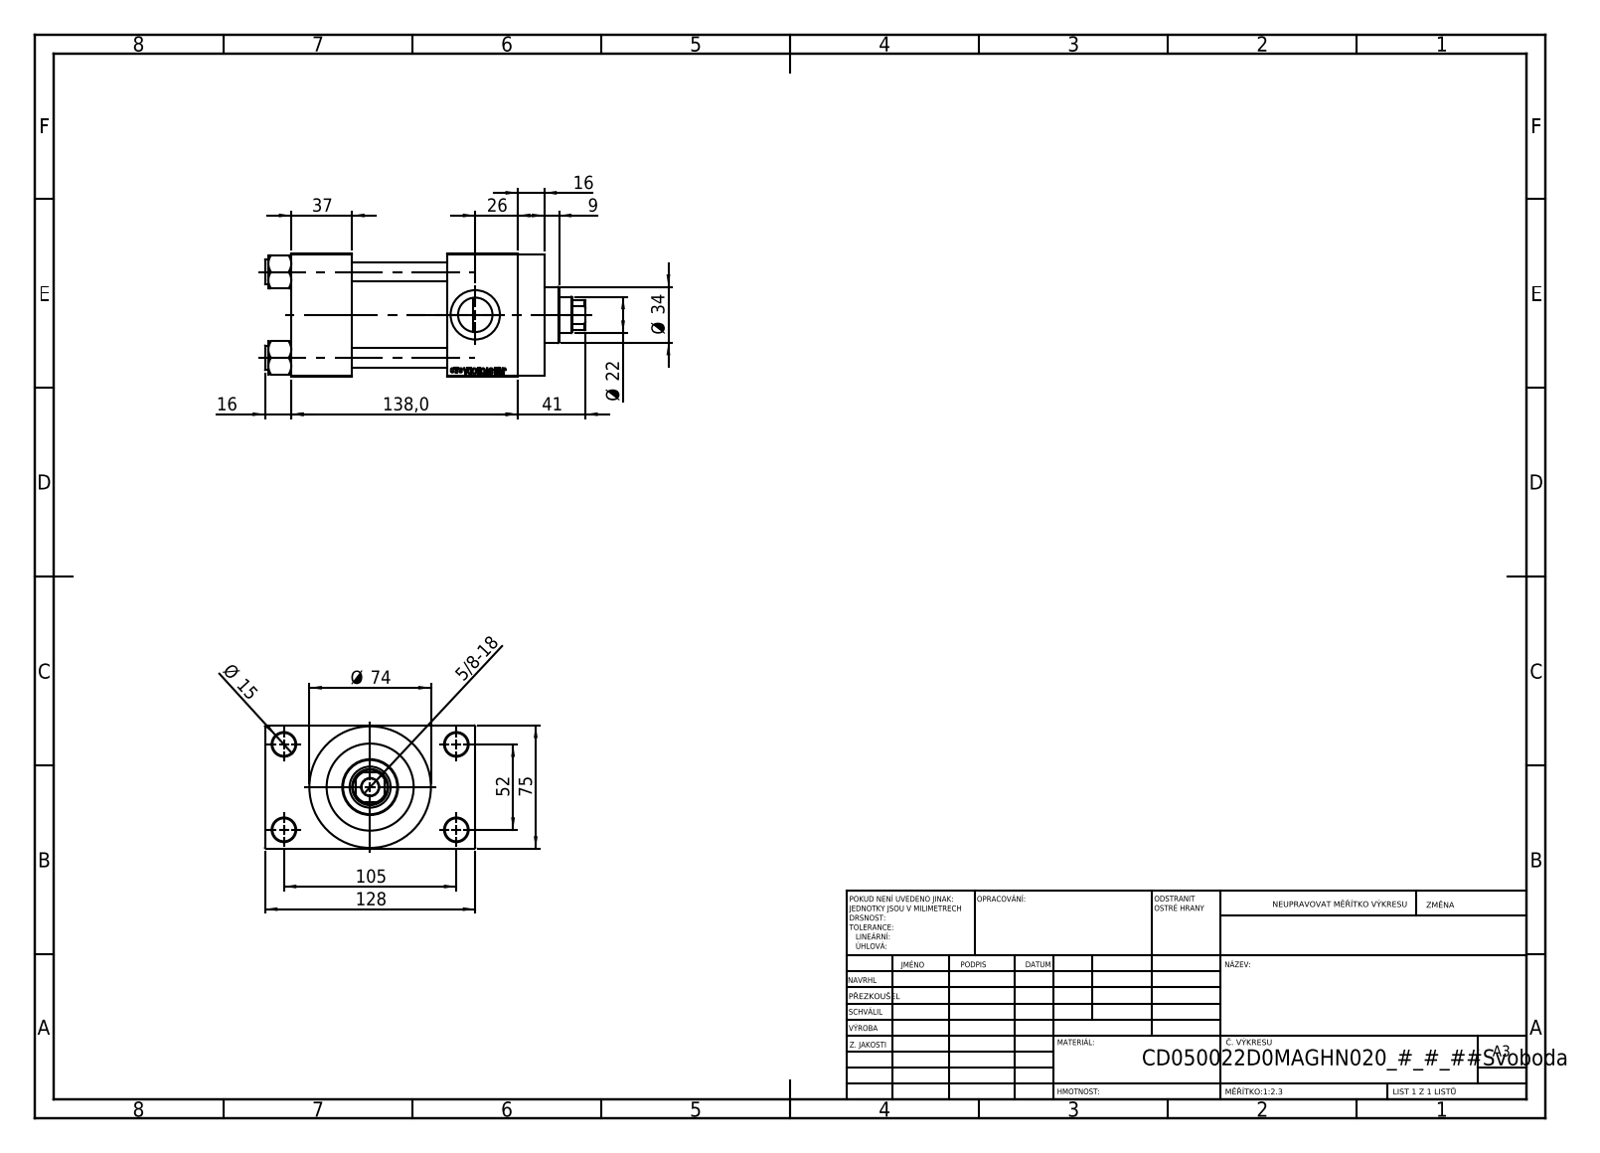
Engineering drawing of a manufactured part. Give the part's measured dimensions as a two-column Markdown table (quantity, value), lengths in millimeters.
| quantity | value |
| --- | --- |
| part name | V215CD_NUT_M5_D; V215CD_VC_A; V215CD_D_Body; V215CD_D_TYCINKA (+1 more) |
| STEP written by | SolidWorks 2019 (CONFIG_CONTROL_DESIGN) |
| units | millimeters |
| bodies | 11 solids, 1104 faces (497 planar, 89 cylindrical, 518 other) |
| overall size | 195 × 128 × 75 |
| volume | 797 396 mm³ |
| surface area | 166 692 mm² |
| round holes (diameter × count) | 12 × 4, 14 × 4, 7 × 2, 20.96 × 2, 30 × 2, 10.5 × 1, 22 × 1, 25 × 1, 41 × 1, 50 × 1, 53 × 1 |
| round bosses / shafts (diameter × count) | 15 × 4, 74 × 1, 56 × 1, 34 × 1 |
| partial cylindrical surfaces (radius × count) | 10.5 × 1 |
| main face-to-face distances | 75, 58, 37, 95, 26.5, 101.5, 138, 101, 43, 16 |
| hole center spacings | 26.35, 36.98, 52.3, 58.43, 58.59, 78.65, 94.37, 52 |
